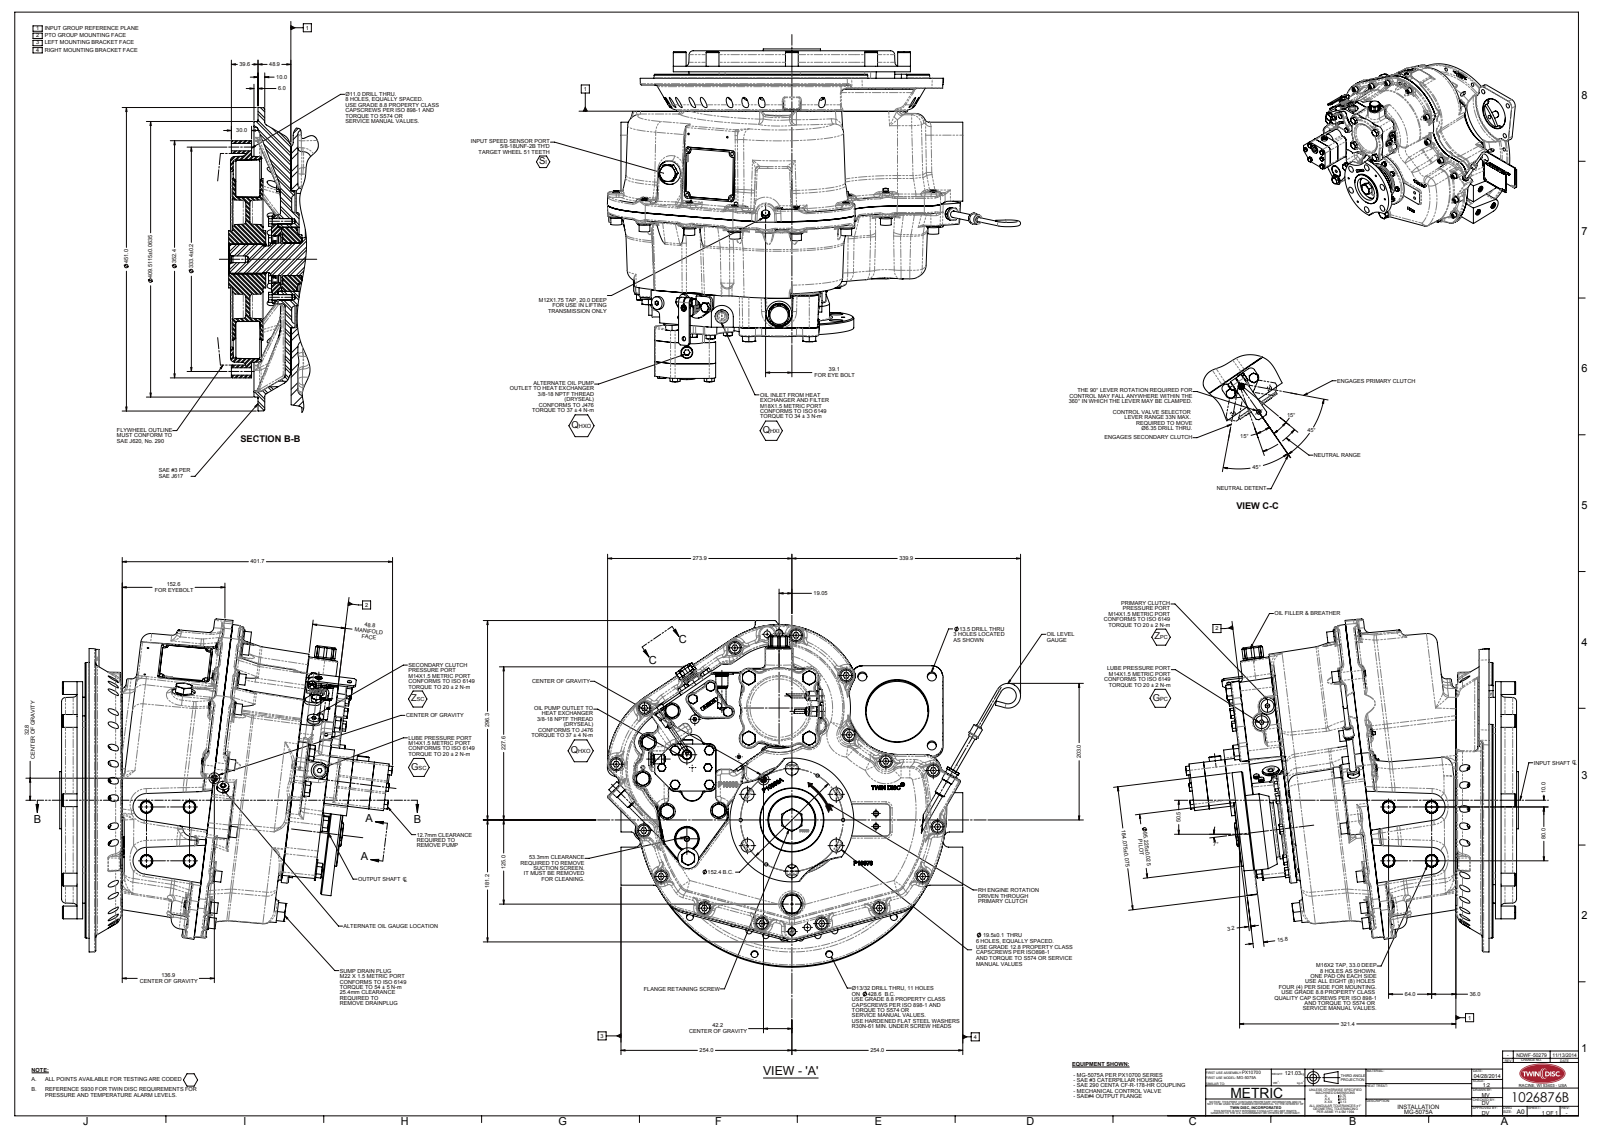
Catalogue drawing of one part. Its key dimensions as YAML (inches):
part_name: "1026876B"
step_written_by: "SolidWorks 2010 (AUTOMOTIVE_DESIGN)"
units: inches
bodies: {solids: 0, faces: 4088, planar: 1027, cylindrical: 833, other: 2228}
overall_size: [28.387, 19.485, 19.473]
round_holes:
  - {diameter: 0.406, count: 11}
  - {diameter: 0.433, count: 8}
  - {diameter: 0.768, count: 6}
  - {diameter: 0.197, count: 4}
  - {diameter: 0.741, count: 4}
  - {diameter: 0.315, count: 3}
  - {diameter: 0.394, count: 3}
  - {diameter: 0.531, count: 3}
  - {diameter: 0.12, count: 2}
  - {diameter: 0.209, count: 2}
  - {diameter: 0.421, count: 2}
  - {diameter: 0.438, count: 2}
round_bosses_or_shafts:
  - {diameter: 0.781, count: 17}
  - {diameter: 0.63, count: 17}
  - {diameter: 0.748, count: 12}
  - {diameter: 0.394, count: 11}
  - {diameter: 0.945, count: 5}
  - {diameter: 0.625, count: 5}
  - {diameter: 0.25, count: 3}
  - {diameter: 16.123, count: 1}
partial_cylinders:
  - {radius: 0.157, count: 52}
  - {radius: 0.079, count: 50}
  - {radius: 0.428, count: 37}
  - {radius: 0.098, count: 36}
  - {radius: 0.118, count: 26}
  - {radius: 0.315, count: 26}
  - {radius: 0.059, count: 25}
  - {radius: 0.591, count: 18}
face_to_face_distances: [0.017, 4.642, 4.659, 0.335, 0.351, 0.015, 0.018, 2.301, 4.643, 4.66]
hole_center_spacings: [8.437, 3, 11.932, 14.614, 16.3, 2.7, 4.284, 5.023]
